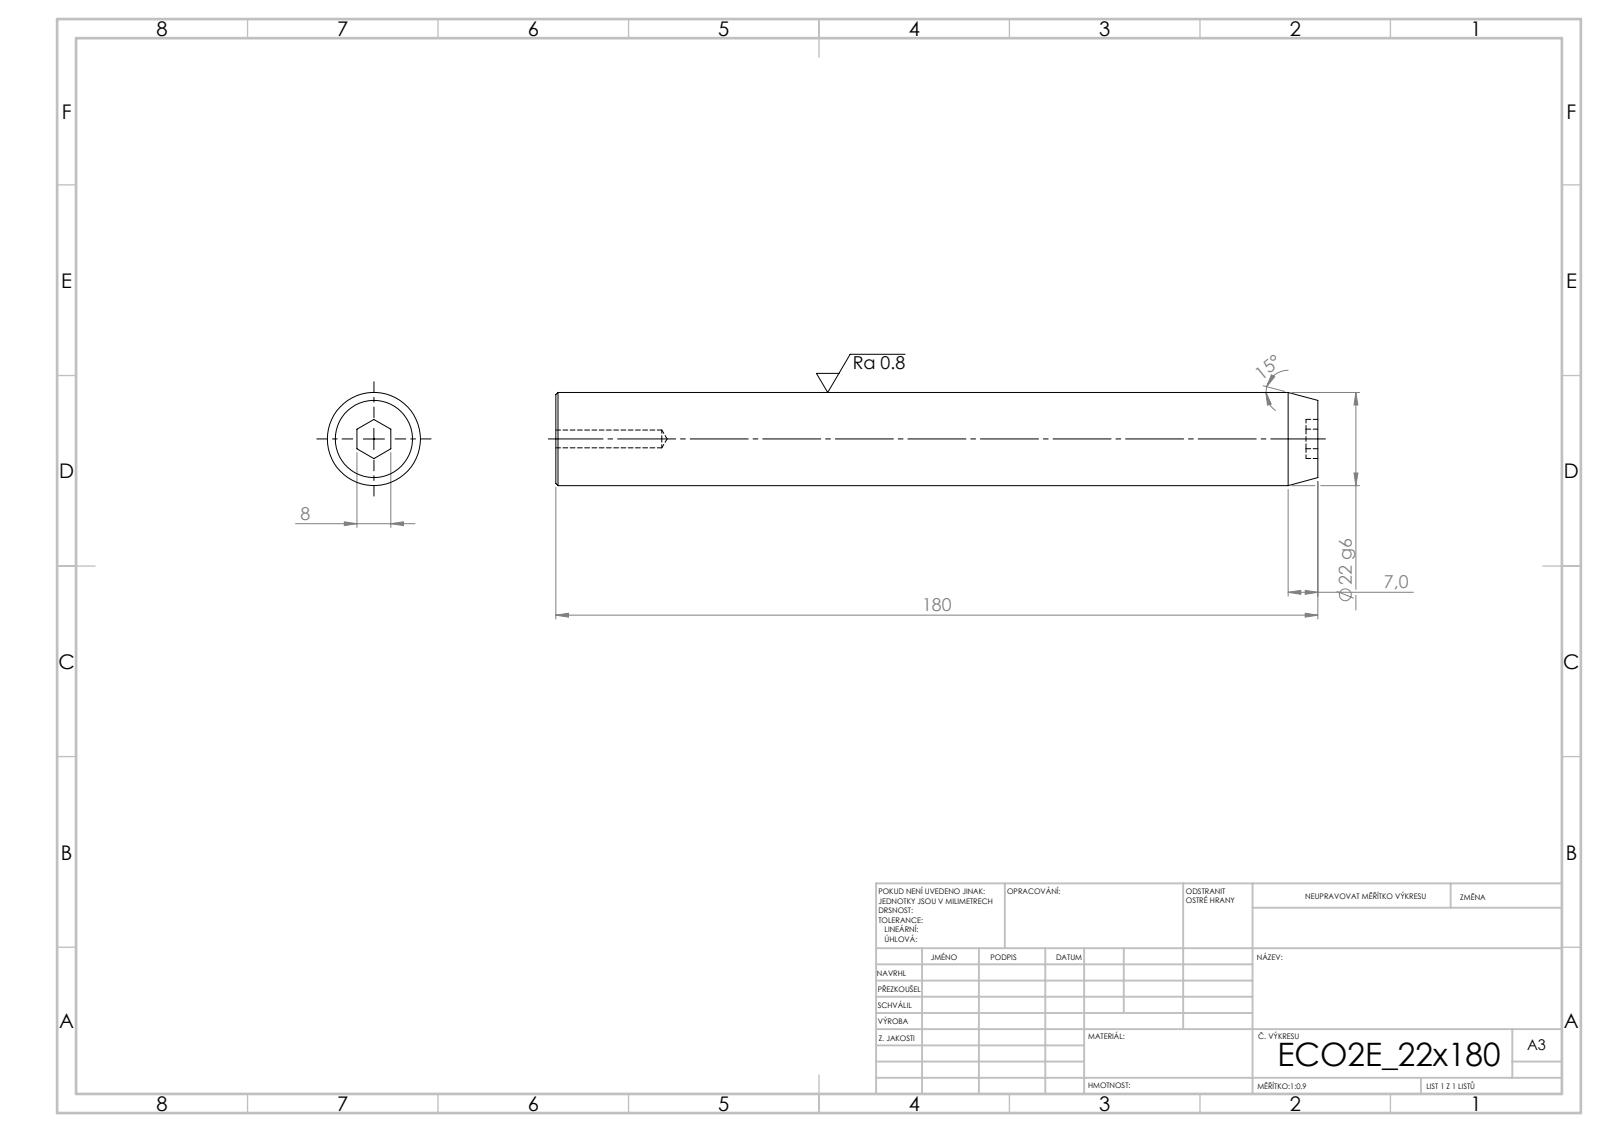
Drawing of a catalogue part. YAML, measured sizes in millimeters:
step_written_by: "SolidWorks 2019 (CONFIG_CONTROL_DESIGN)"
units: millimeters
bodies: {solids: 1, faces: 19, planar: 9, cylindrical: 4, other: 6}
overall_size: [180, 22, 22]
volume: 67480
surface_area: 13446
round_holes:
  - {diameter: 4.2, count: 1}
round_bosses_or_shafts:
  - {diameter: 22, count: 1}
face_to_face_distances: [180, 2.8, 177.2, 8]
